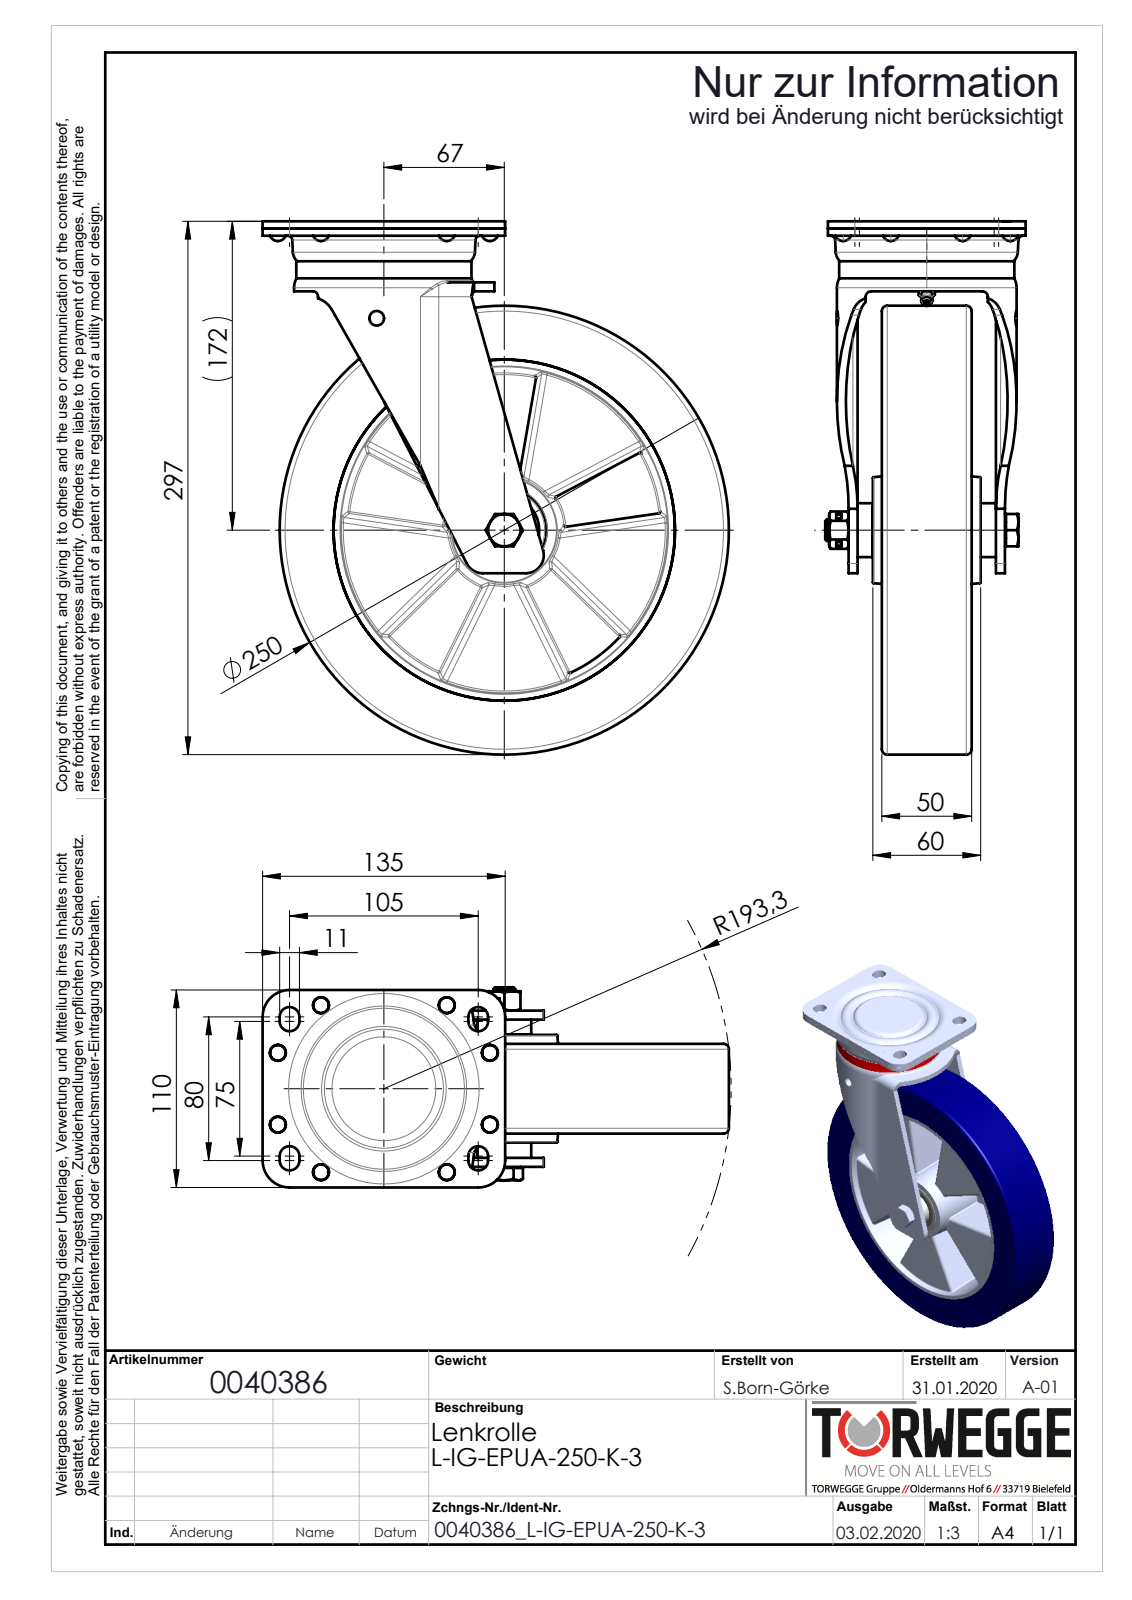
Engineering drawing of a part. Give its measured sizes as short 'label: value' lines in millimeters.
name: 0040386_L-IG-EPUA-250-K-3_(A-01)
written by: SolidWorks 2018 (AUTOMOTIVE_DESIGN)
unit: mm
bodies: 0 solids, 750 faces (182 planar, 198 cylindrical, 370 other)
size: 297 × 259.5 × 111.5
holes: 1× ⌀1.5, 1× ⌀8.2, 1× ⌀10.2, 1× ⌀12, 1× ⌀12.5, 1× ⌀20, 1× ⌀20.5, 1× ⌀25.2, 1× ⌀25.5, 1× ⌀28.1, 1× ⌀38.9, 1× ⌀42
bosses: 2× ⌀21, 1× ⌀250, 1× ⌀97.5, 1× ⌀30, 1× ⌀24, 1× ⌀18
rounds: 24× R3, 20× R1, 8× R5.5, 6× R0.3, 4× R15, 2× R8, 2× R10, 2× R25
face distances: 5, 44.5, 24, 58, 5.5, 50, 29, 10.5, 13.5, 68.5
hole spacings: 137.71
